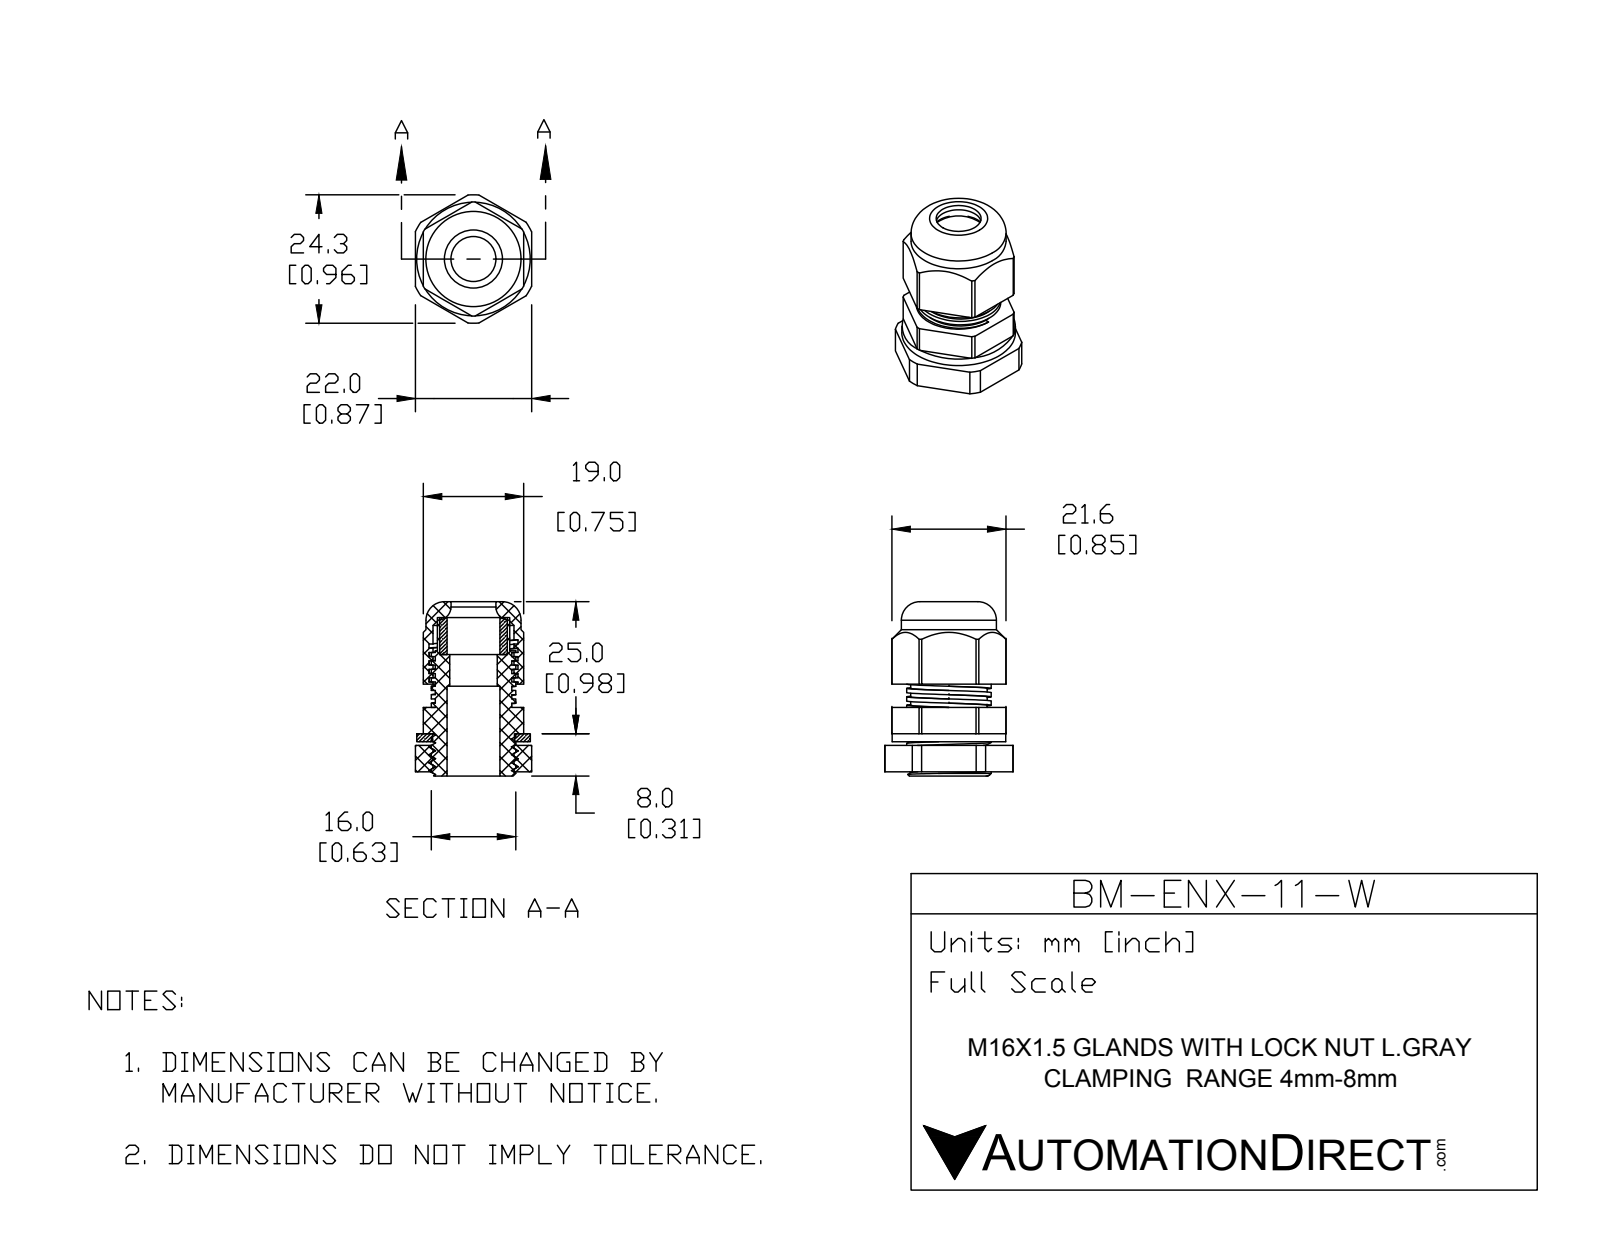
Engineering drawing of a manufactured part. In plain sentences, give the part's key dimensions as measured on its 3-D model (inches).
The part is named "BM-ENX-11-W". Its 3-D file was written by "SolidWorks 2015 (CONFIG_CONTROL_DESIGN)". It is 5 solids with 242 faces: 133 planar, 87 cylindrical and 22 other. Overall it measures 1.299 by 0.957 by 0.866 inches. Its volume is 0.415 cubic inches and its surface area 12.97 square inches. Round holes: 1 of diameter 0.335, 1 of diameter 0.354, 1 of diameter 0.394, 1 of diameter 0.504, 1 of diameter 0.604, 1 of diameter 0.61. Round bosses or shafts: 1 of diameter 0.846, 1 of diameter 0.709, 1 of diameter 0.63, 1 of diameter 0.539. Partial cylindrical surfaces (rounded edges, fillets, slot ends): 1 of radius 0.425, 1 of radius 0.478. The main face-to-face distances are 0.059, 0.748, 0.197, 0.283, 0.807, 0.256, 0.087, 0.866, 0.028, 0.224.
